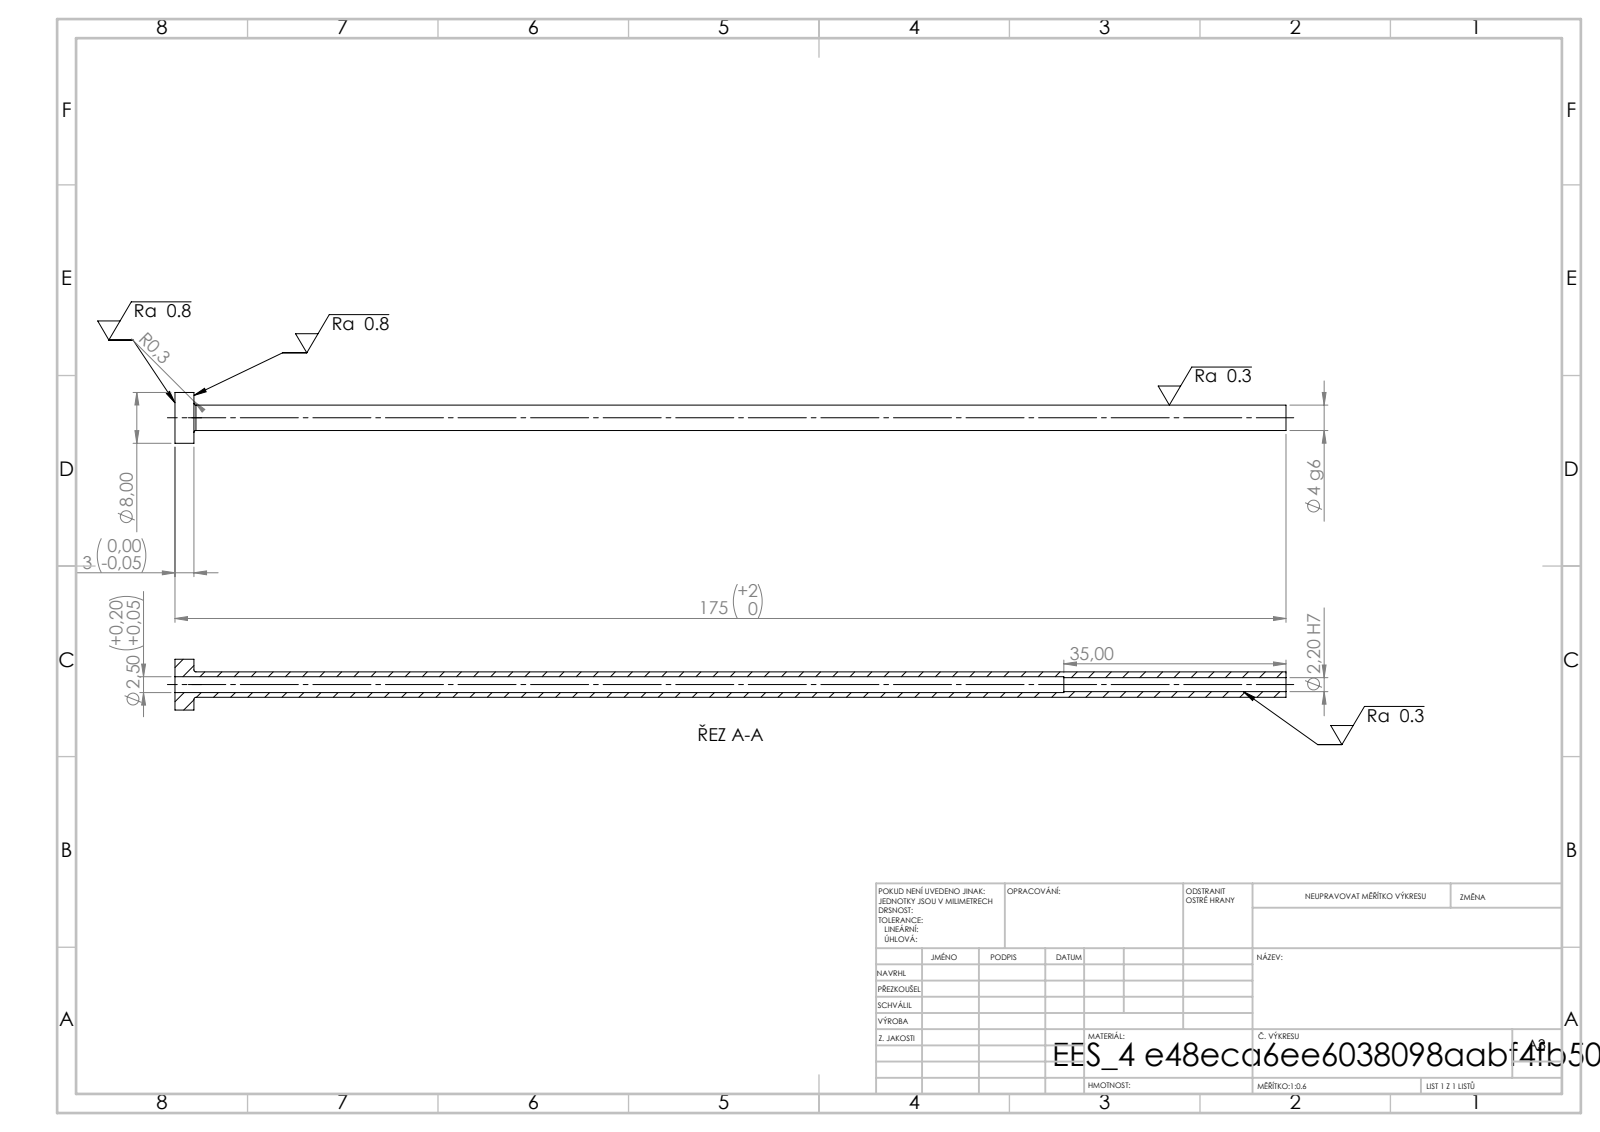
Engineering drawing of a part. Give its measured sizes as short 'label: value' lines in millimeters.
written by: SolidWorks 2019 (CONFIG_CONTROL_DESIGN)
unit: mm
bodies: 1 solid, 14 faces (4 planar, 8 cylindrical, 2 other)
size: 175 × 8 × 8
volume: 1 492 mm³; area: 3 670 mm²
holes: 1× ⌀2.2, 1× ⌀2.5
bosses: 1× ⌀8, 1× ⌀4
face distances: 3, 175, 172, 140, 137, 35
